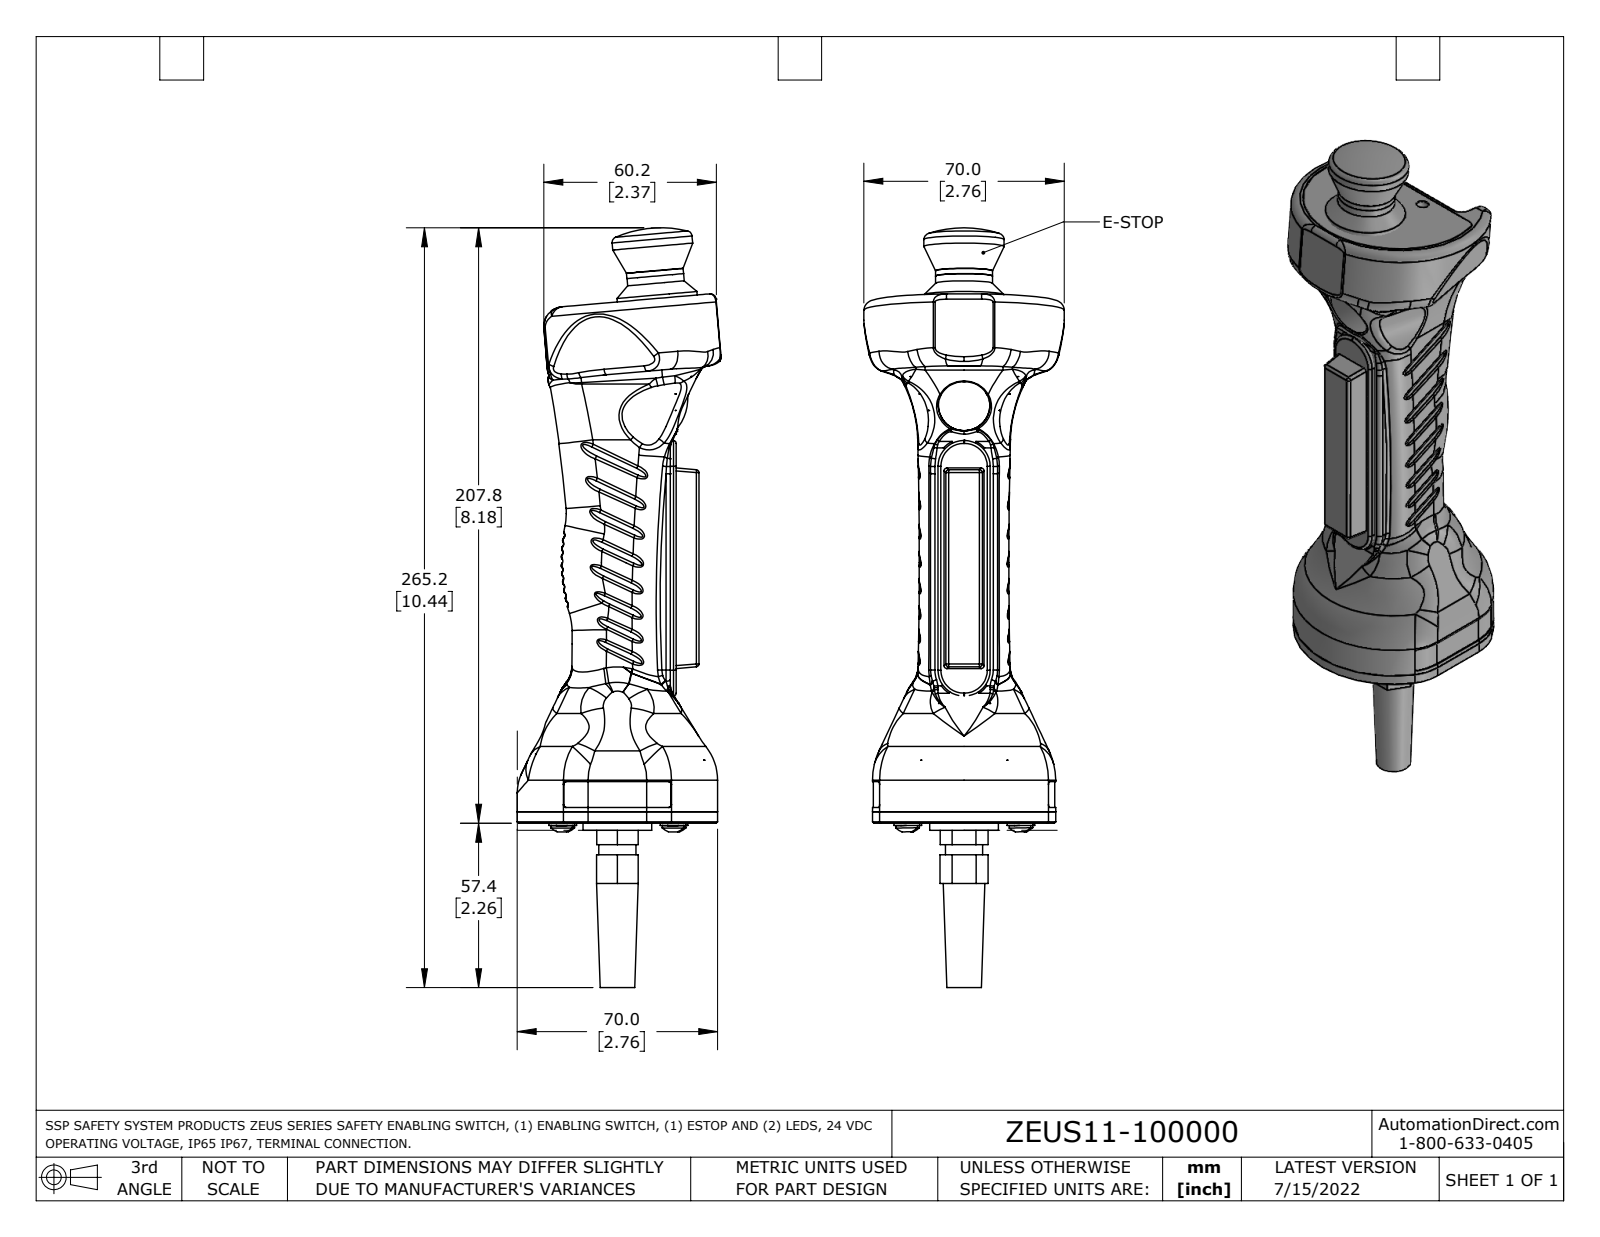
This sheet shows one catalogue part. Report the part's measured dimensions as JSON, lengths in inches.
{"part_name": "ZEUS11-100000", "step_written_by": "SolidWorks 2021 (AUTOMOTIVE_DESIGN)", "units": "inches", "bodies": {"solids": 19, "faces": 1144, "planar": 324, "cylindrical": 401, "other": 419}, "overall_size": [10.442, 2.803, 2.756], "volume_in3": 24.17, "surface_area_in2": 125.6, "round_holes": [[0.132, 4], [0.169, 4], [0.177, 4], [0.197, 4], [0.098, 2], [0.11, 2], [0.165, 2], [0.173, 2], [0.331, 2], [0.551, 1], [0.709, 1], [0.728, 1]], "round_bosses_or_shafts": [[0.354, 4], [0.295, 4], [0.157, 4], [0.039, 4], [1.102, 2], [0.781, 2], [0.236, 2], [0.945, 1]], "partial_cylinders_radius": [[0.005, 96], [0.039, 51], [0.028, 48], [0.079, 21], [0.118, 10], [0.031, 7], [0.012, 5], [0.618, 4]], "face_to_face_distances": [0.157, 0.079, 0.02, 0.014, 0.065, 0.059, 0.098, 0.177, 0.571, 0.256], "hole_center_spacings": [0.404, 0.63, 0.867, 1.08, 1.181, 1.531, 1.558, 0.513]}
